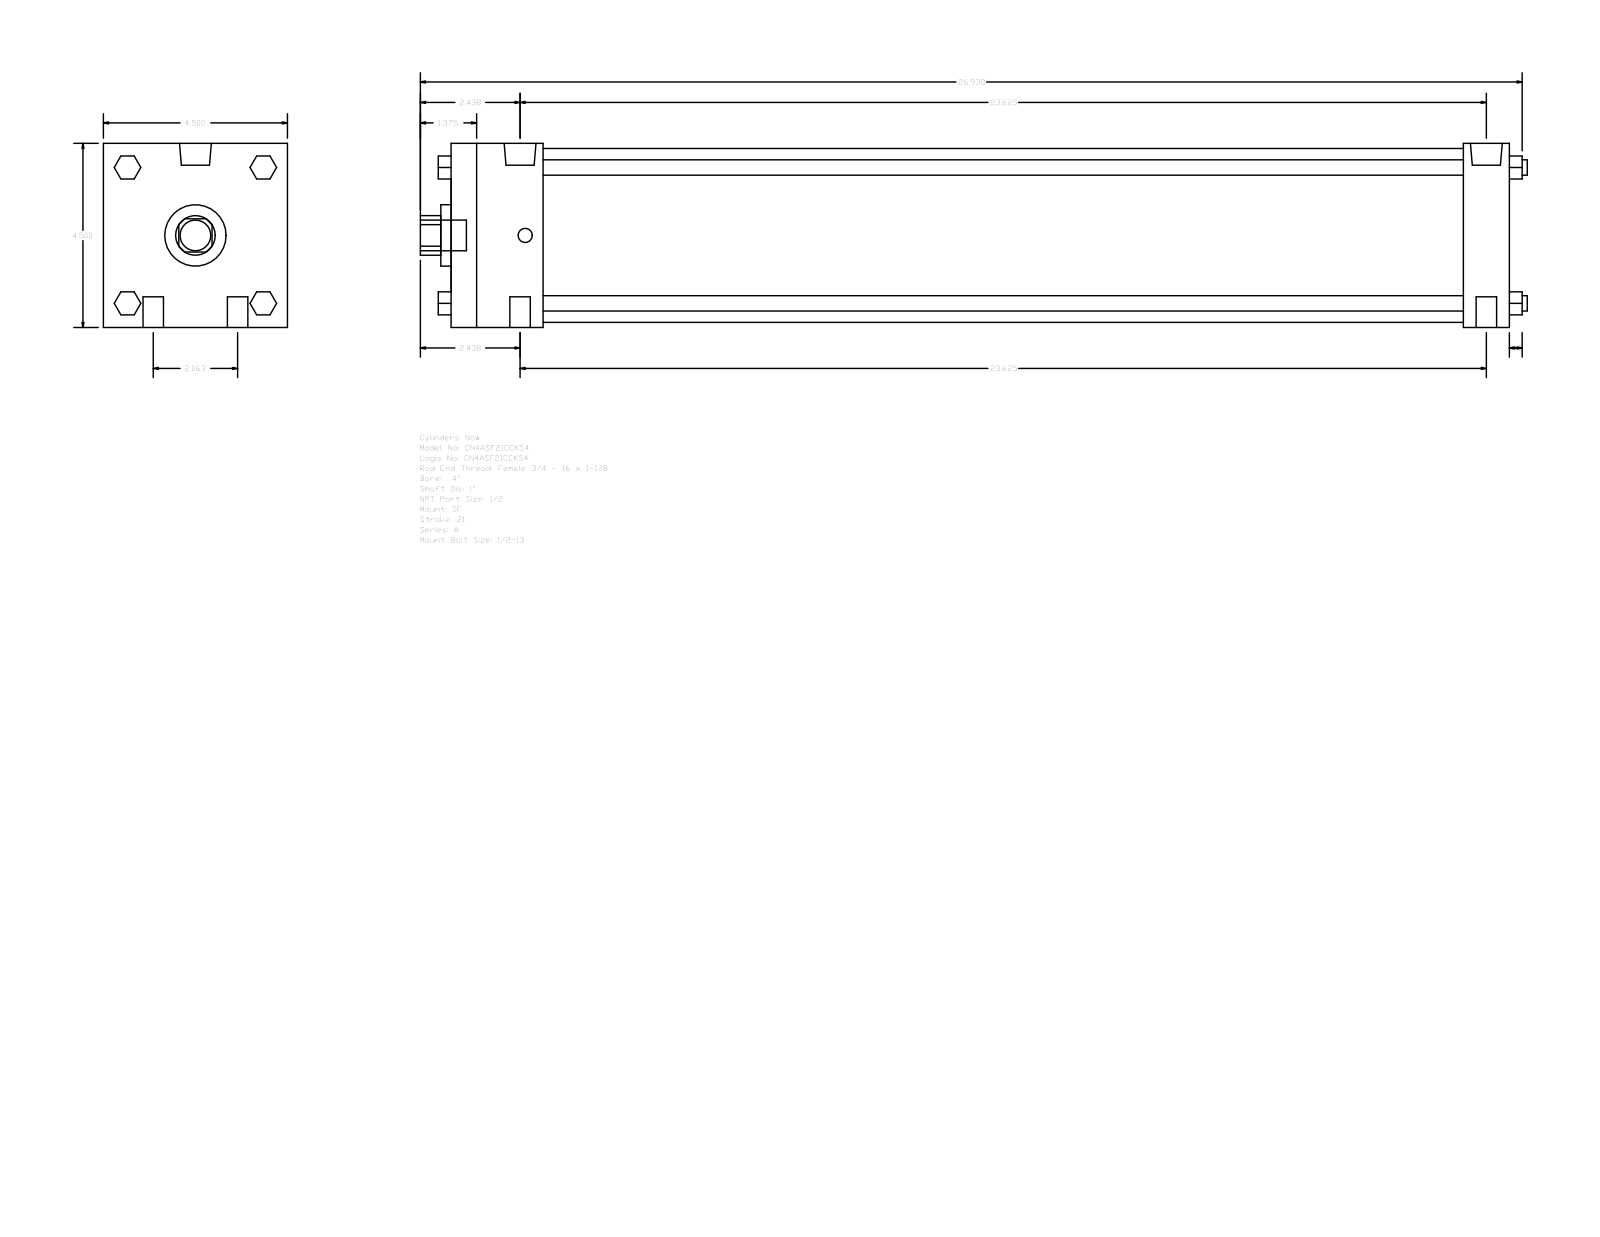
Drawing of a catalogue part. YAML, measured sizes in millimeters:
part_name: "A_SF__0400_1"
step_written_by: "GSSL Pune (CONFIG_CONTROL_DESIGN)"
units: millimeters
bodies: {solids: 0, faces: 124, planar: 94, cylindrical: 30, other: 0}
overall_size: [687.39, 114.3, 114.3]
round_holes:
  - {diameter: 25.4, count: 1}
  - {diameter: 38.1, count: 1}
  - {diameter: 107.95, count: 1}
round_bosses_or_shafts:
  - {diameter: 12.7, count: 4}
  - {diameter: 9.53, count: 4}
  - {diameter: 19.77, count: 2}
  - {diameter: 8.73, count: 2}
  - {diameter: 19.05, count: 1}
partial_cylinders:
  - {radius: 12.29, count: 1}
face_to_face_distances: [114.3, 657.22, 28.57, 628.65, 57.15, 571.5, 600.07, 14.29, 42.16, 73.03]
